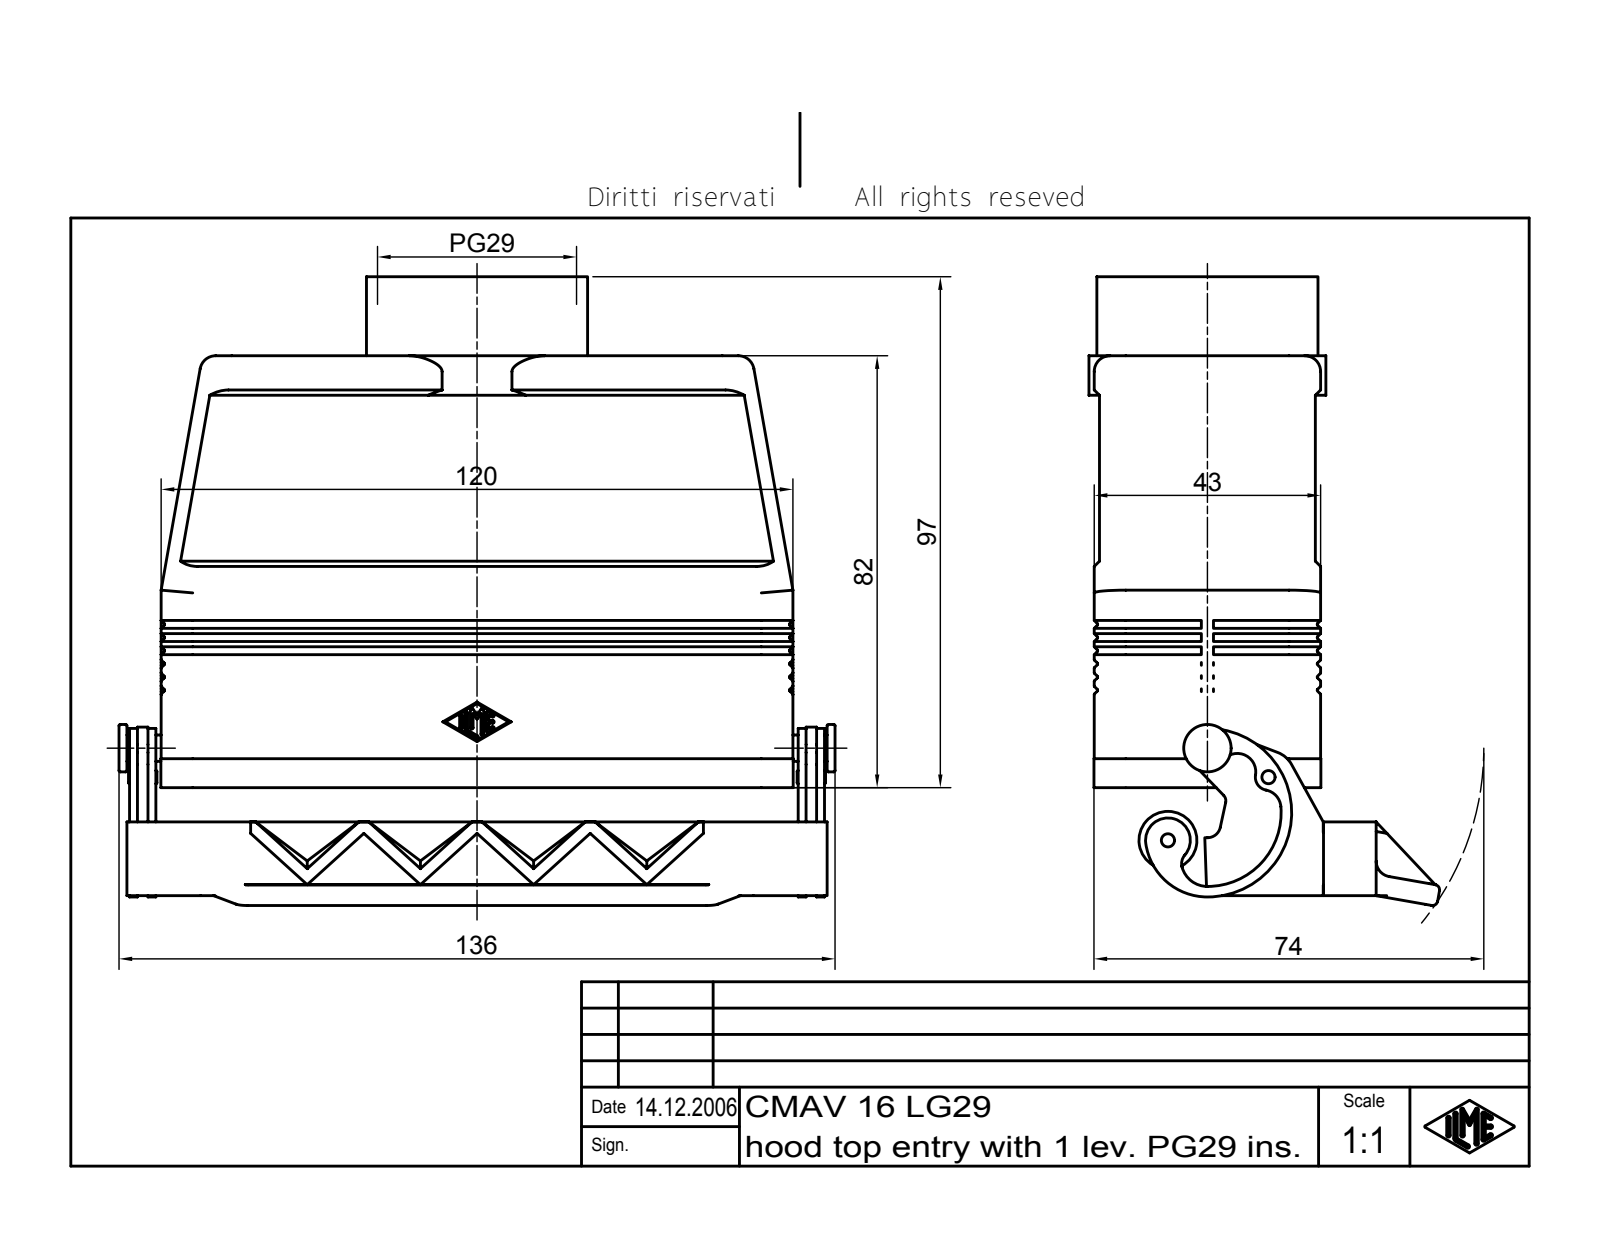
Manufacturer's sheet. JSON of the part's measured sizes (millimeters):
{"part_name": "CMAV 16 LG29", "step_written_by": "Autodesk Inventor 7 (AUTOMOTIVE_DESIGN)", "units": "millimeters", "bodies": {"solids": 1, "faces": 960, "planar": 235, "cylindrical": 324, "other": 401}, "overall_size": [136, 119.37, 66.59], "volume_mm3": 126203, "surface_area_mm2": 74939, "round_holes": [[2.5, 1], [33.48, 1], [35.48, 1]], "round_bosses_or_shafts": [[45, 1], [42, 1], [11, 1], [9, 1], [5, 1], [3.1, 1], [2, 1]], "partial_cylinders_radius": [[0.2, 52], [0.25, 32], [2.5, 9], [6, 8], [3, 7], [1, 6], [2.45, 4], [6.05, 4]], "face_to_face_distances": [3.45, 3.5, 39.55, 39.5, 36.05, 36, 36.1, 2.5, 2.45, 1]}
